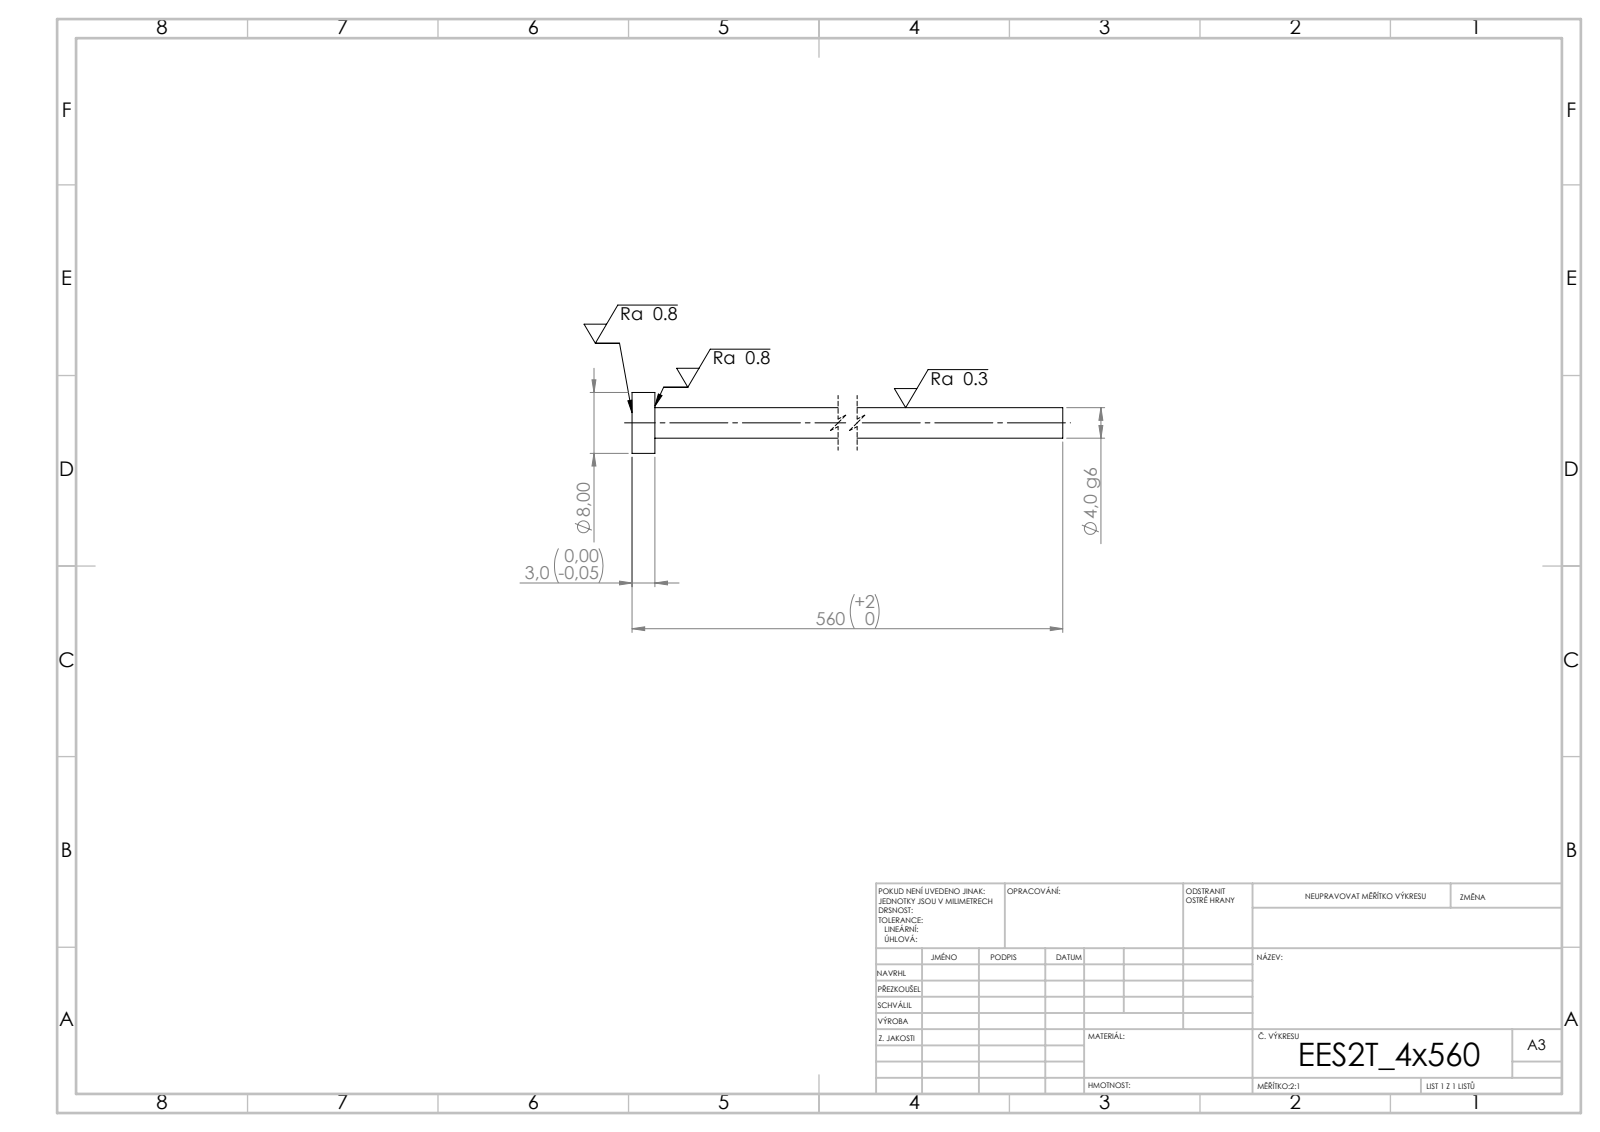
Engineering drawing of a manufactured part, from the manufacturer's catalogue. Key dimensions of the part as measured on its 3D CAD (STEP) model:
STEP written by: SolidWorks 2019 (CONFIG_CONTROL_DESIGN)
Units: millimetres
Bodies: 1 solid, 7 faces (3 planar, 4 cylindrical, 0 other)
Overall size (bounding box): 560 × 8 × 8
Volume: 7 150 mm³ · Surface area: 7 175 mm²
Round bosses / shafts (diameter × count): ⌀8 ×1, ⌀4 ×1
Main face-to-face distances: 3, 560, 557
